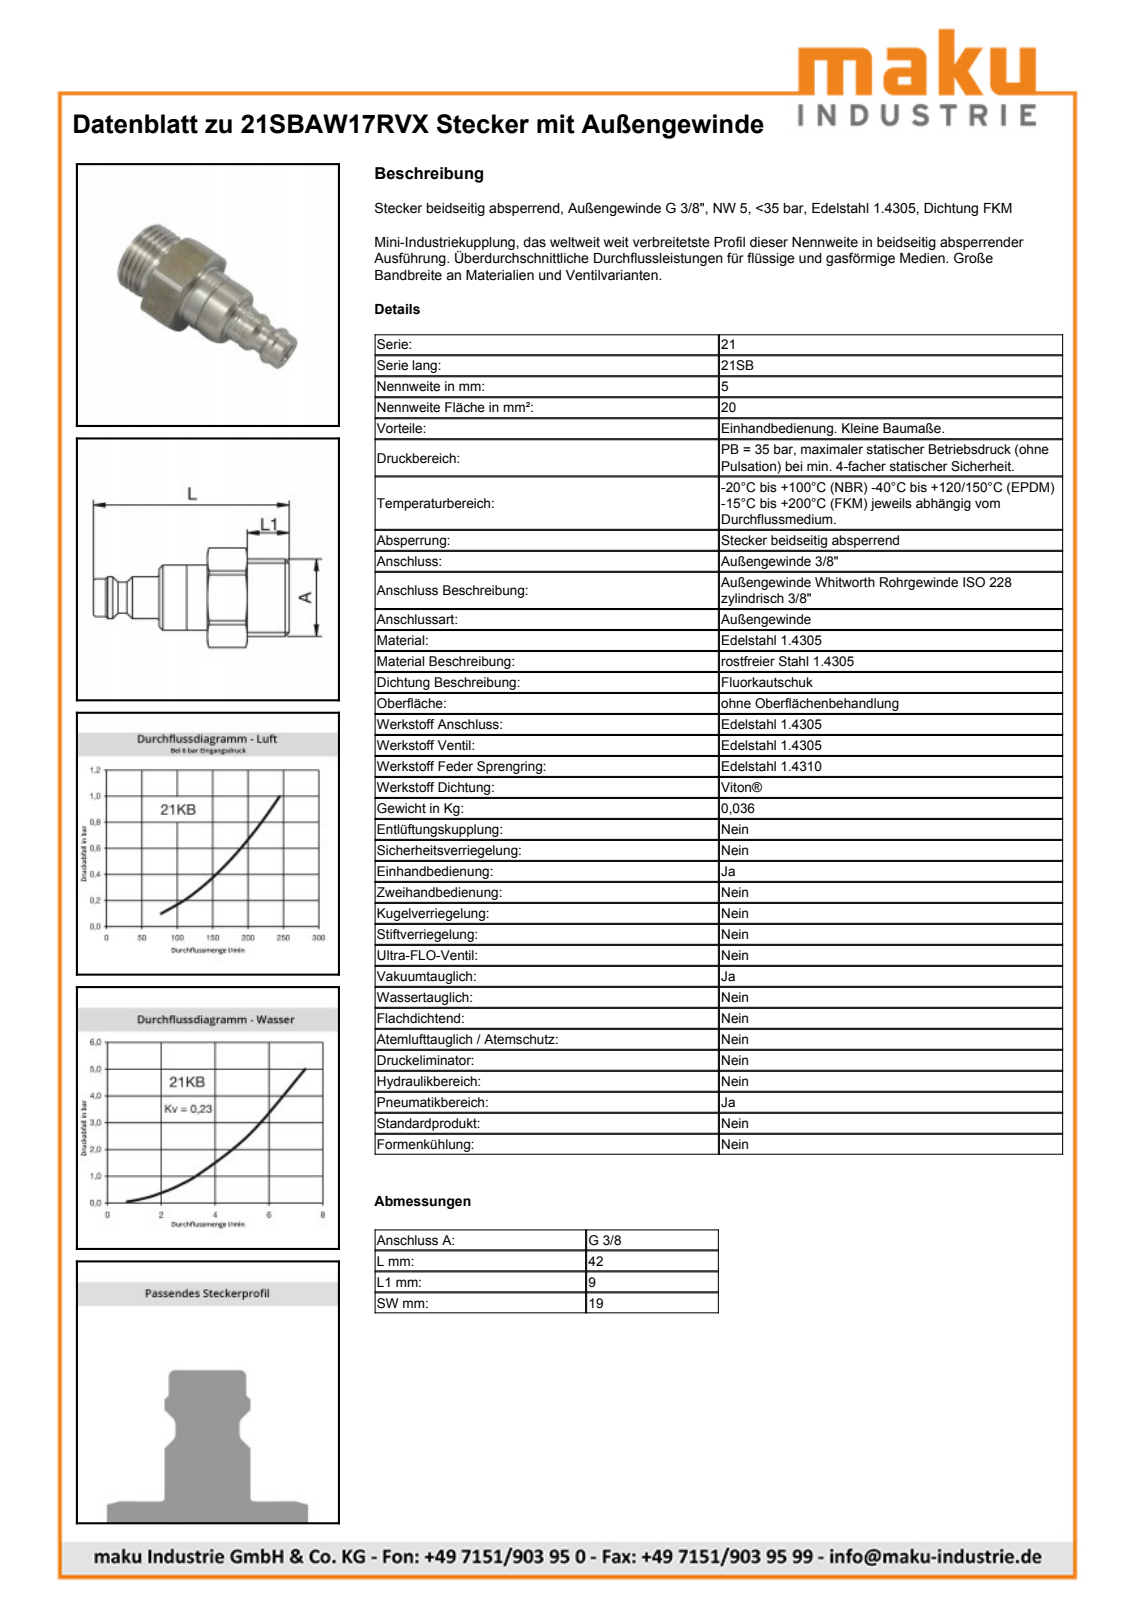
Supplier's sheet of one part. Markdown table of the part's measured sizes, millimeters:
| quantity | value |
| --- | --- |
| part name | D106163 |
| STEP written by | Autodesk Inventor 2011 (AUTOMOTIVE_DESIGN) |
| units | millimeters |
| bodies | 1 solid, 57 faces (14 planar, 16 cylindrical, 27 other) |
| overall size | 42 × 21.31 × 20.18 |
| volume | 6 831 mm³ |
| surface area | 2 722 mm² |
| round holes (diameter × count) | 12 × 1 |
| round bosses / shafts (diameter × count) | 16.66 × 1, 14 × 1, 11.26 × 1, 9 × 1, 8.1 × 1, 6.7 × 1 |
| partial cylindrical surfaces (radius × count) | 10.7 × 1 |
| main face-to-face distances | 19, 17.55, 9, 8.55, 10.35, 18.9, 27.9, 14.1, 24.45, 33 |
